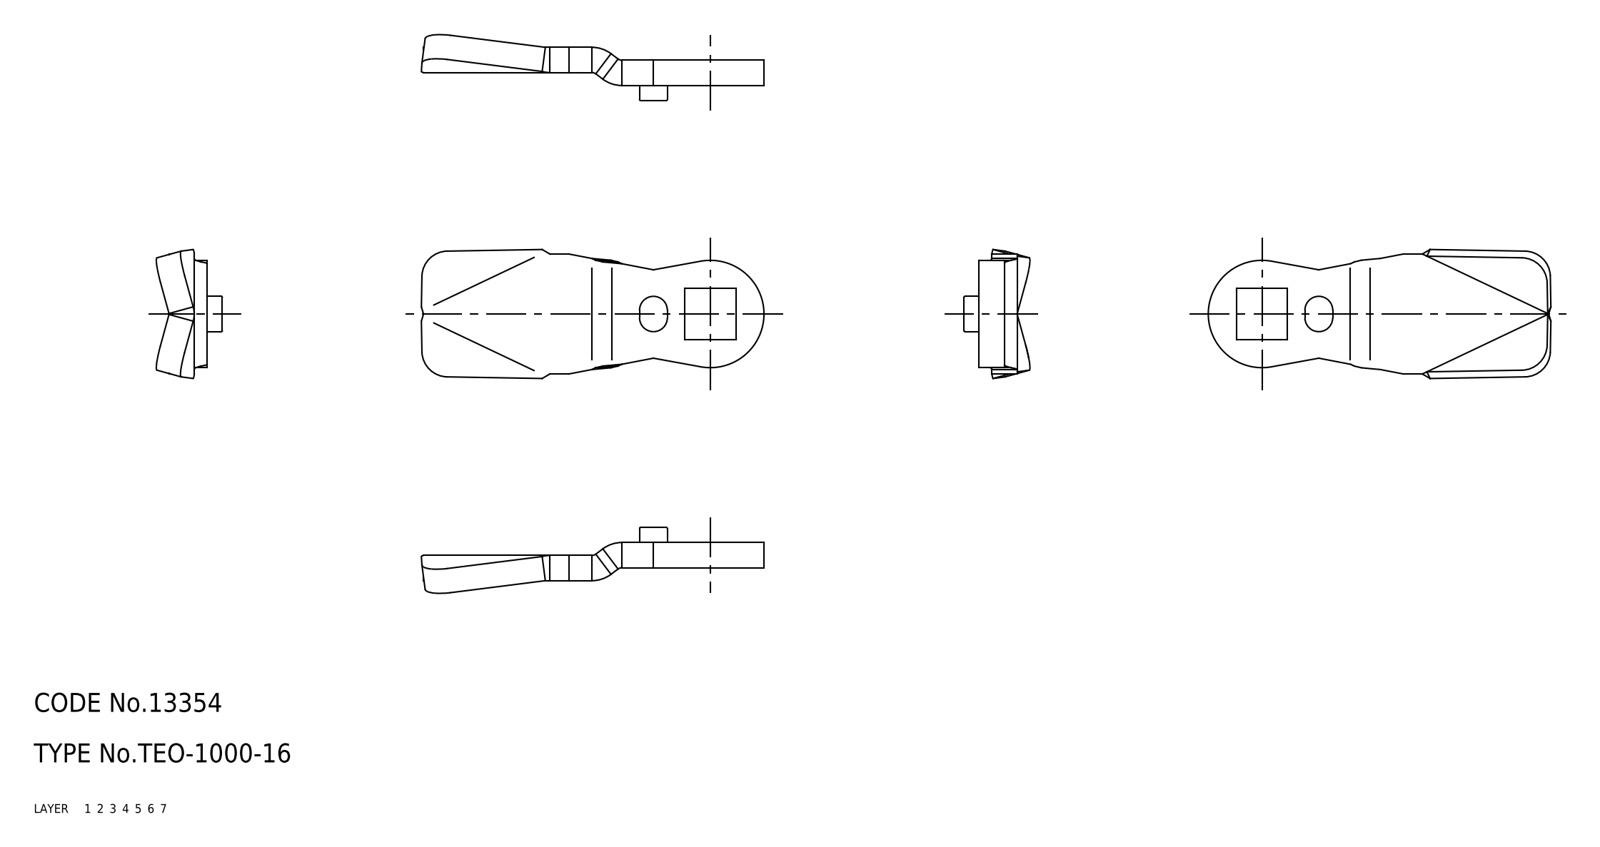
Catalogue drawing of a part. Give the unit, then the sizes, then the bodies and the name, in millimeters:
Units: millimetres
Overall size (bounding box): 53.96 × 20.94 × 11.86
Volume: 3 573 mm³ · Surface area: 2 557 mm²
Bodies: 1 solid, 55 faces (0 planar, 0 cylindrical, 55 other)
Part name (STEP PRODUCT): cam
STEP written by: CADfix (AUTOMOTIVE_DESIGN)
